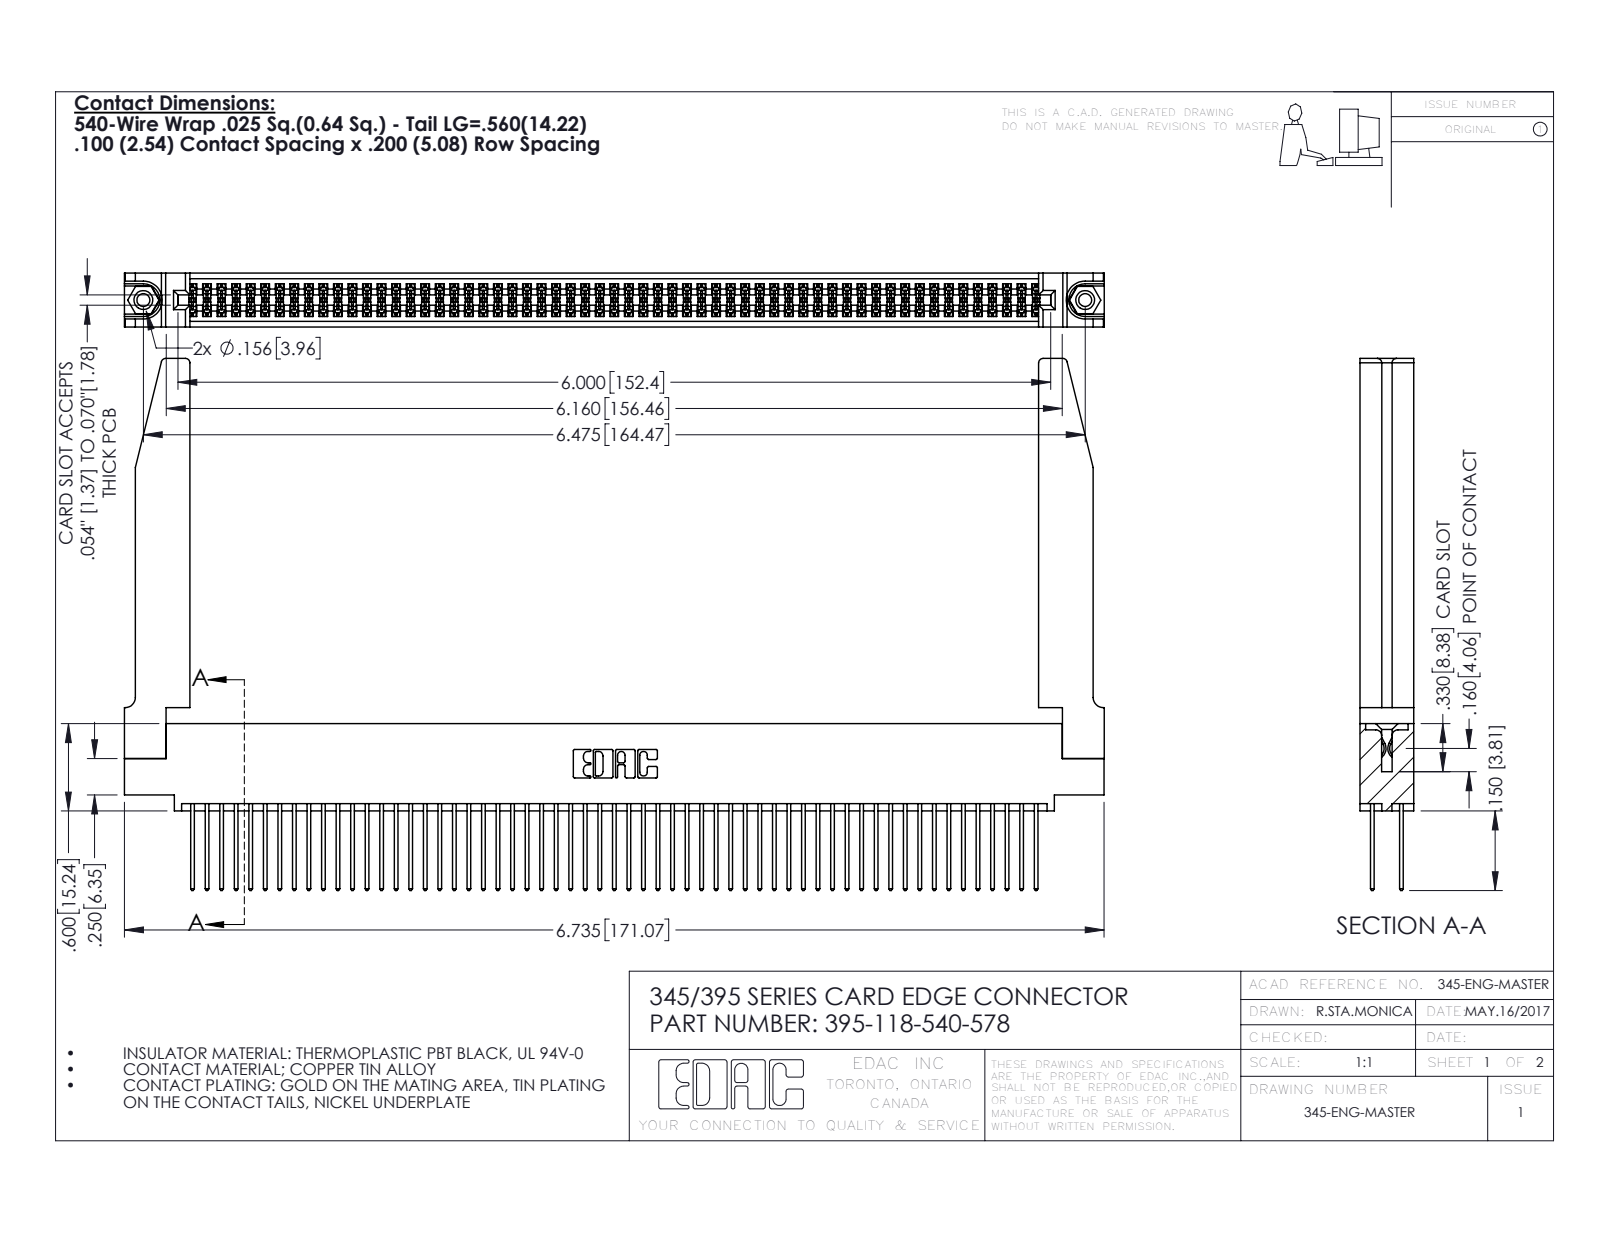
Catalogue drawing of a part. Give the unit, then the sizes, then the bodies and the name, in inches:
Units: inches
Overall size (bounding box): 6.736 × 3.657 × 0.37
Round holes (diameter × count): ⌀0.089 ×2, ⌀0.125 ×2, ⌀0.156 ×2, ⌀0.064 ×1
Round bosses / shafts (diameter × count): ⌀0.155 ×2
Partial cylindrical surfaces — rounded edges, fillets, slot ends (radius × count): R0.006 ×177, R0.01 ×118, R0.01 ×22, R0.03 ×8, R0.007 ×6, R0.031 ×6, R0.026 ×3, R0.014 ×2
Main face-to-face distances: 0.072, 0.298, 0.37, 0.098, 0.272, 0.025, 0.2, 0.225, 0.175, 0.148
Hole centre spacings: 0.27, 6.239, 6.475
Volume: 1.521 in³ · Surface area: 53.77 in²
Bodies: 123 solids, 6264 faces (4120 planar, 2092 cylindrical, 52 other)
Part name (STEP PRODUCT): 345-250-001_345-250-001-102; 345-292-001_345-293-140; 395-118-540-578; 345-220-078_345-220-078 (+1 more)
STEP written by: SolidWorks 2016 (CONFIG_CONTROL_DESIGN)
